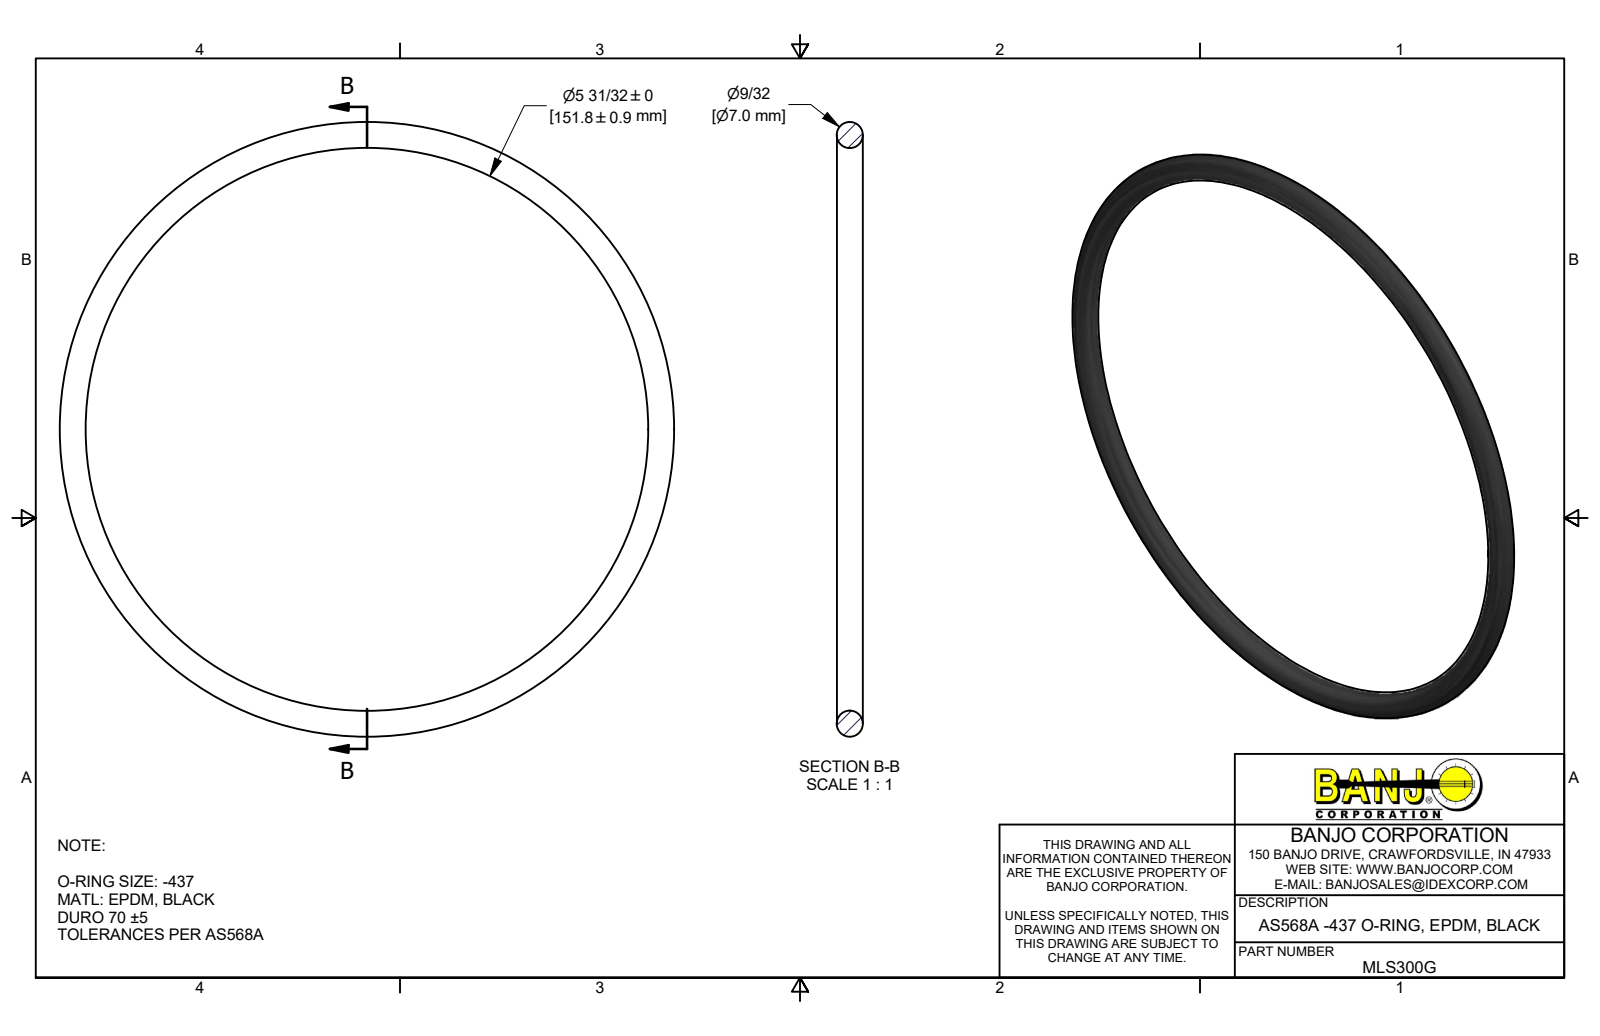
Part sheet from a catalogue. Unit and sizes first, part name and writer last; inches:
Units: inches
Overall size (bounding box): 6.525 × 6.525 × 0.275
Volume: 1.166 in³ · Surface area: 16.96 in²
Bodies: 1 solid, 1 faces (0 planar, 0 cylindrical, 1 other)
Part name (STEP PRODUCT): MLS300G
STEP written by: Autodesk Inventor 2019 (AUTOMOTIVE_DESIGN)
